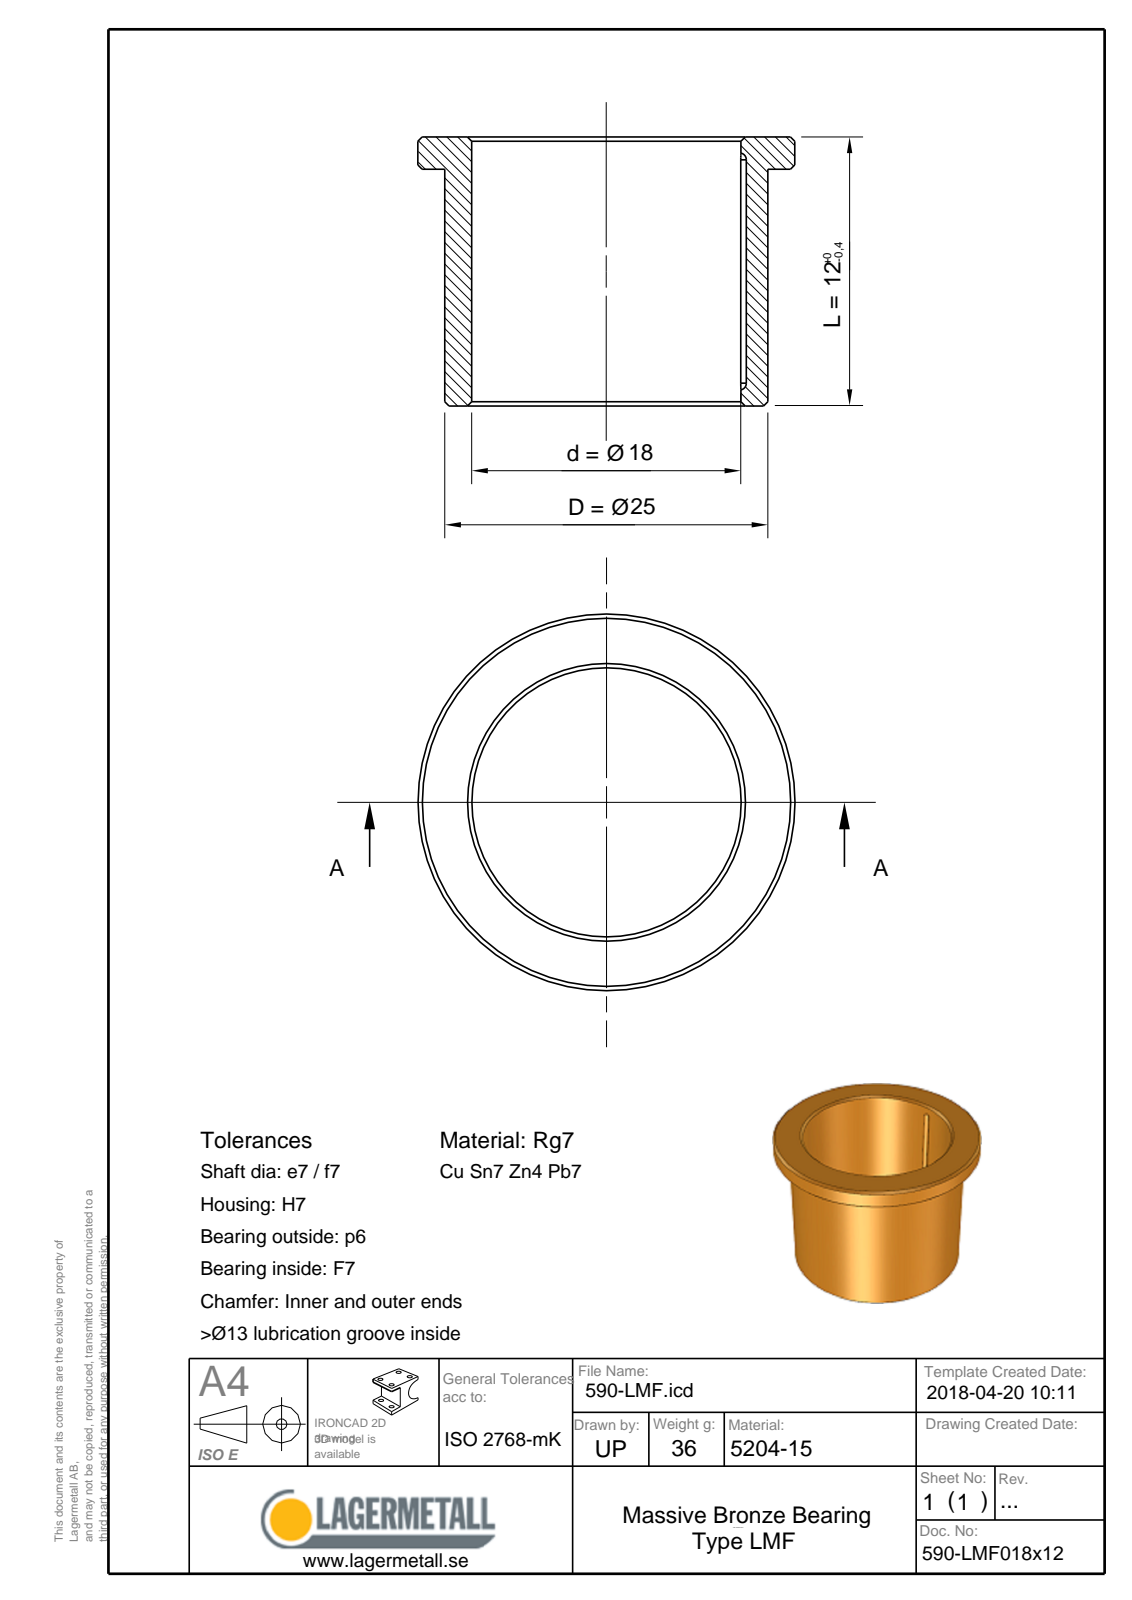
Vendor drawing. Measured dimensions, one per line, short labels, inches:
name: 590-LMF018x12
written by: Spatial InterOp 3D (CONFIG_CONTROL_DESIGN)
unit: in
bodies: 1 solid, 18 faces (5 planar, 6 cylindrical, 7 other)
size: 1.26 × 1.26 × 0.472
volume: 0.246 in³; area: 4.19 in²
holes: 1× ⌀0.709
bosses: 1× ⌀1.26, 1× ⌀0.984
rounds: 3× R0.03
face distances: 0.157, 0.315, 0.472, 0.059
